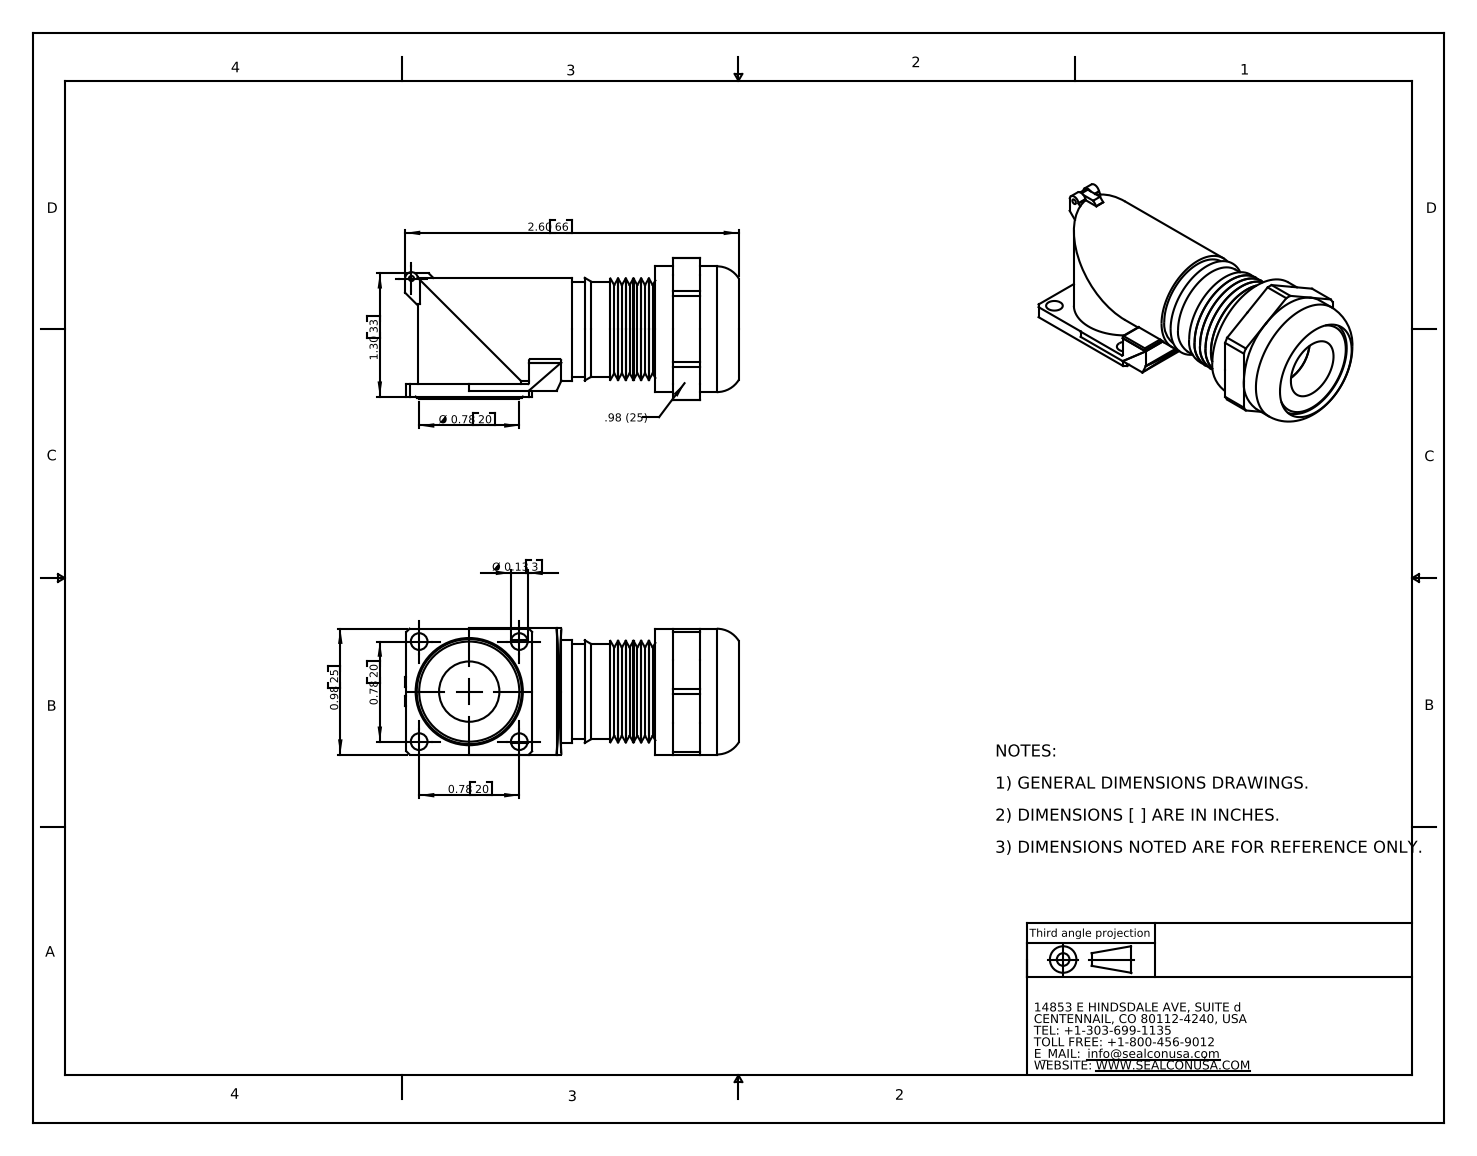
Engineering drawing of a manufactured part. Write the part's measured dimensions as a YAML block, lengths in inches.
part_name: "ED20FA-BR"
step_written_by: "SolidWorks 2007 (CONFIG_CONTROL_DESIGN)"
units: inches
bodies: {solids: 3, faces: 192, planar: 88, cylindrical: 68, other: 36}
overall_size: [2.6, 1.107, 0.984]
volume: 1.056
surface_area: 17.8
round_holes:
  - {diameter: 0.13, count: 4}
  - {diameter: 0.47, count: 2}
  - {diameter: 0.04, count: 1}
round_bosses_or_shafts:
  - {diameter: 0.8, count: 2}
  - {diameter: 0.98, count: 1}
  - {diameter: 0.79, count: 1}
  - {diameter: 0.78, count: 1}
  - {diameter: 0.74, count: 1}
partial_cylinders:
  - {radius: 0.009, count: 3}
  - {radius: 3.047, count: 2}
  - {radius: 0.04, count: 1}
  - {radius: 0.05, count: 1}
  - {radius: 0.553, count: 1}
face_to_face_distances: [0.997, 0.98, 0.096, 0.02, 0.116, 0.65, 0.347, 1.26, 0.61, 0.263]
hole_center_spacings: [0.552, 0.78, 1.104]
